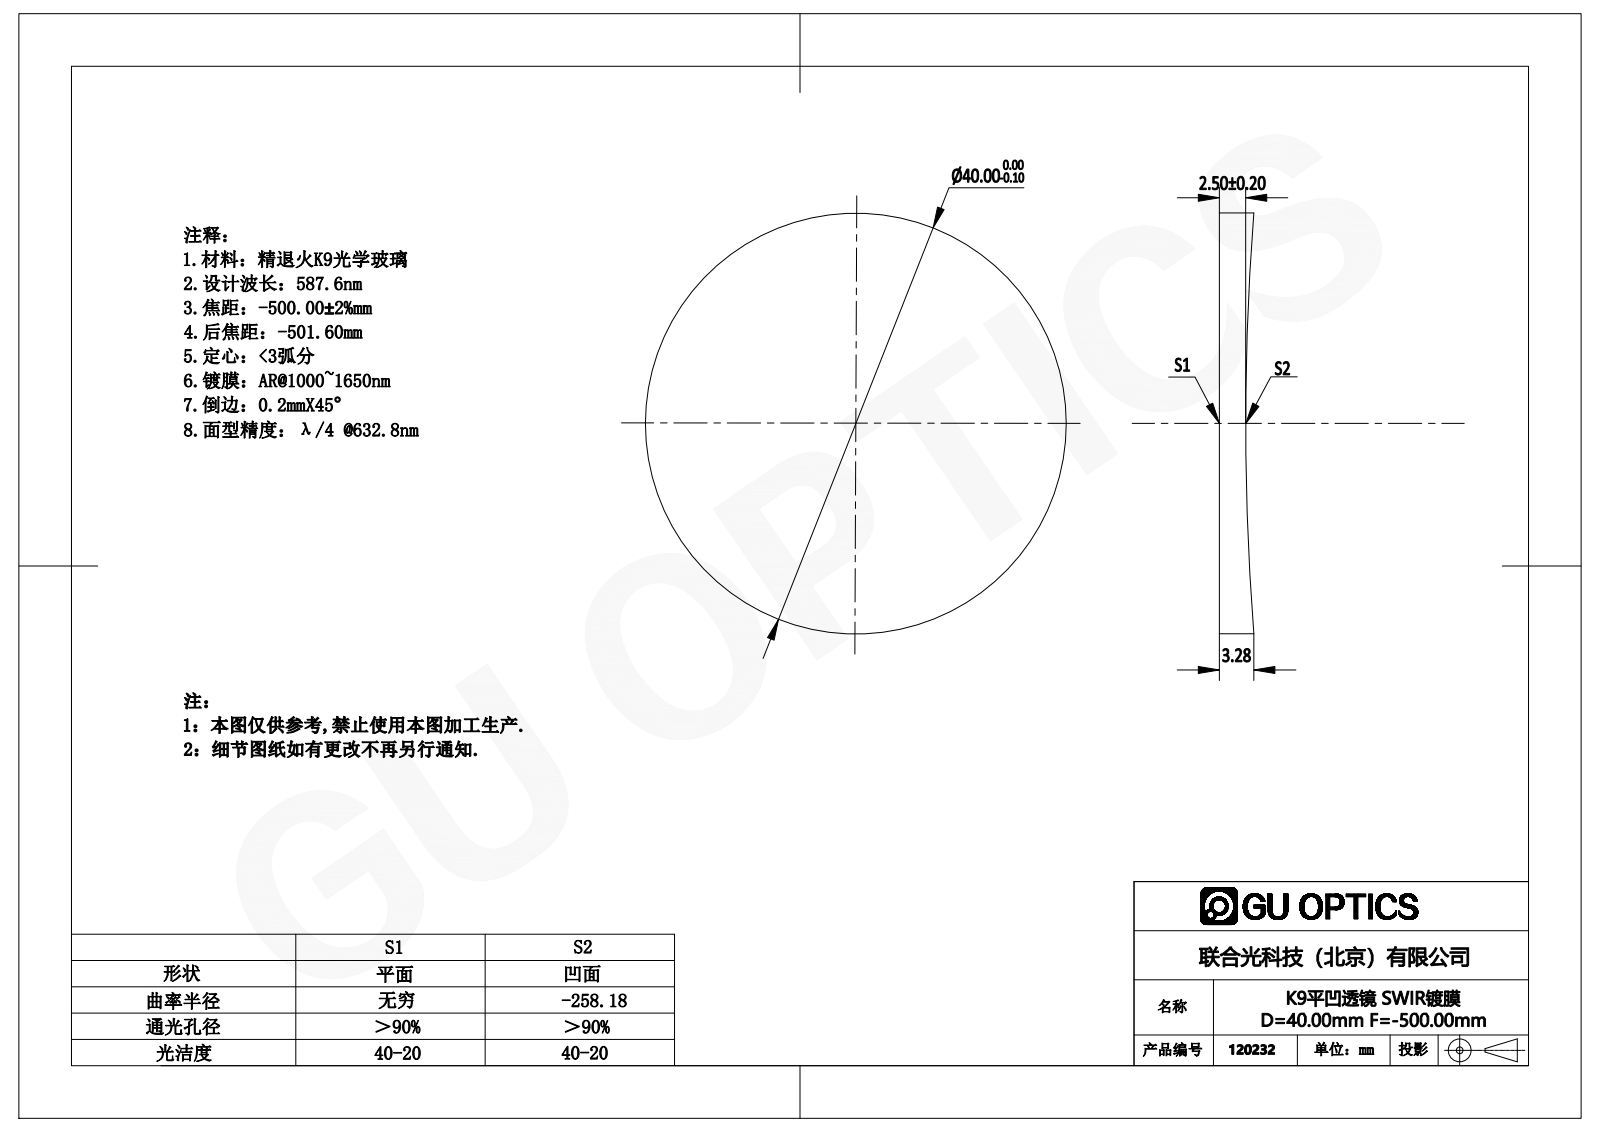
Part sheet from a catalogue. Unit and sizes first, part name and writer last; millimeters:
Units: millimetres
Overall size (bounding box): 40 × 40 × 3.28
Round bosses / shafts (diameter × count): ⌀40 ×1
Volume: 3 629 mm³ · Surface area: 2 927 mm²
Bodies: 1 solid, 5 faces (1 planar, 2 cylindrical, 2 other)
Part name (STEP PRODUCT): 120052
STEP written by: SolidWorks 2016 (AUTOMOTIVE_DESIGN)
